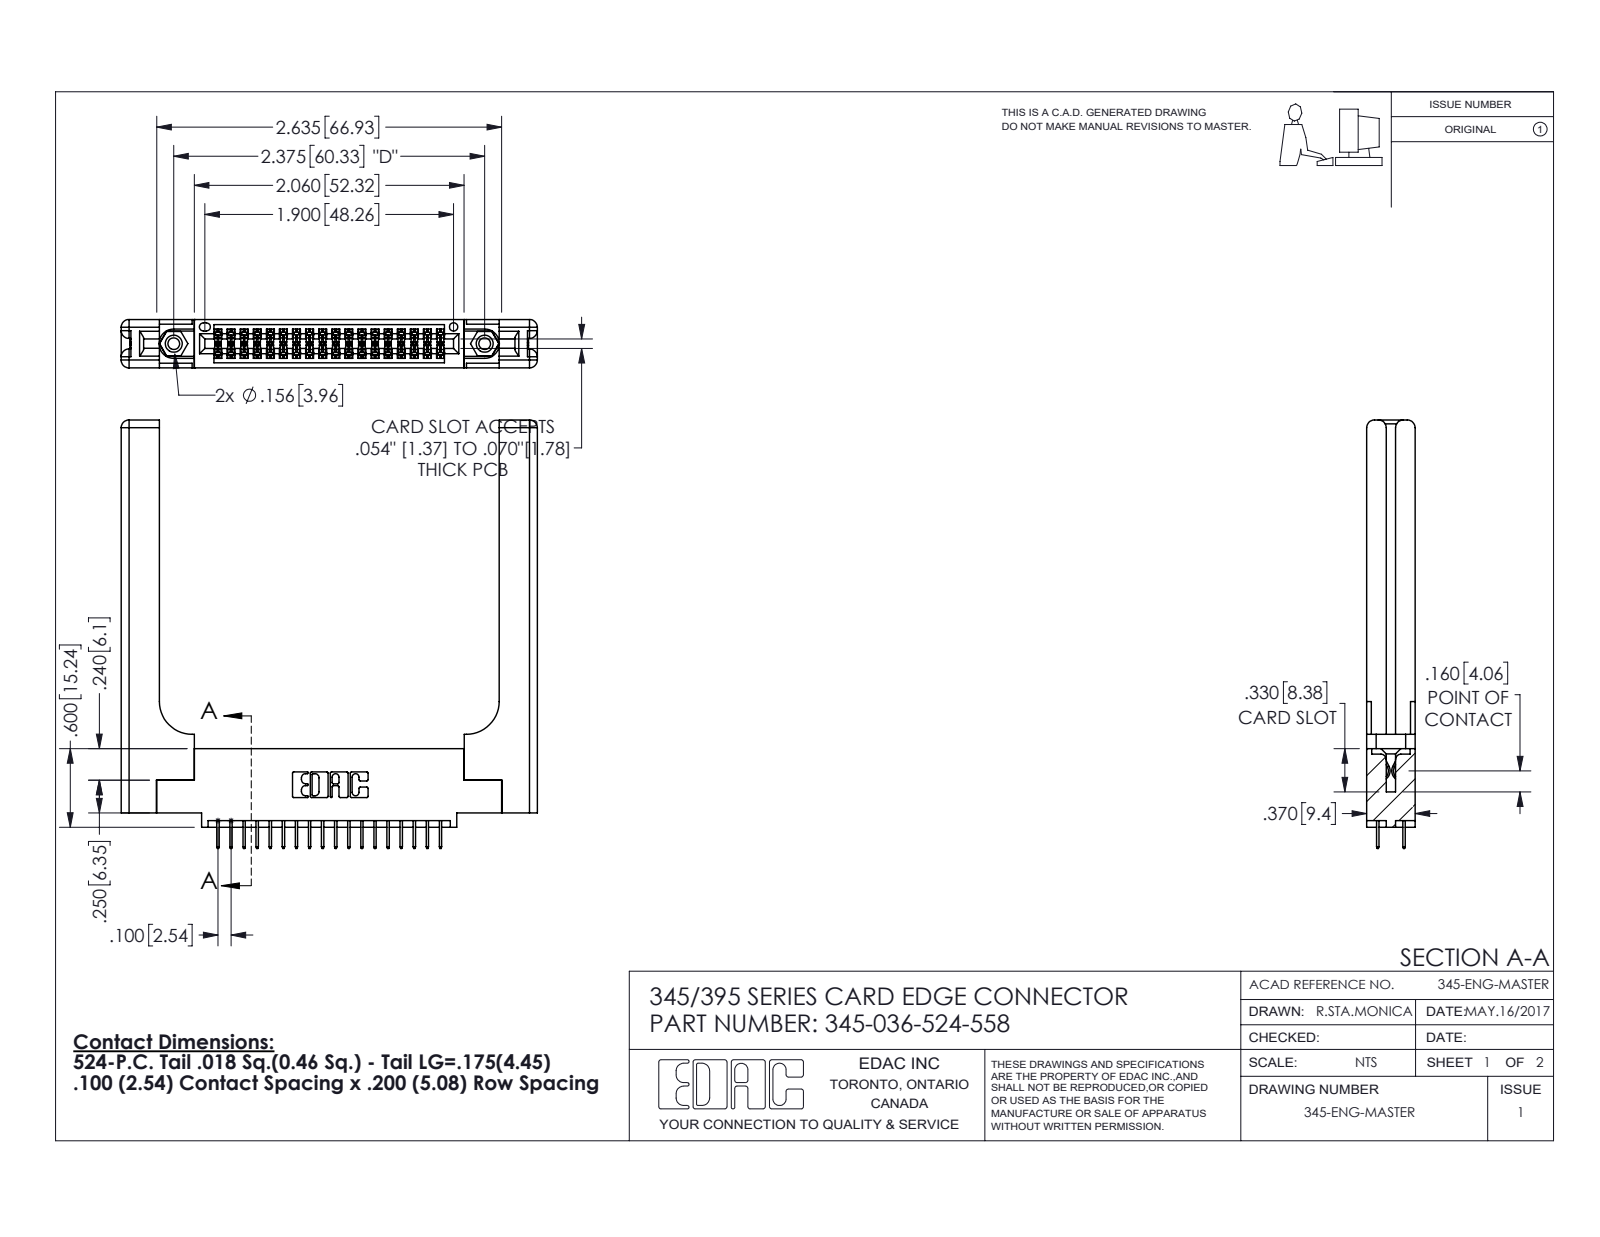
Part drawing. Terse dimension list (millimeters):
name: 345 Part_0.110 Offset - 0.156 Dia-TH; 345-220-058_345-220-058; 345-250-001_345-250-001-102; 345-292-001_345-293-124 (+1 more)
written by: SolidWorks 2016 (CONFIG_CONTROL_DESIGN)
unit: mm
bodies: 41 solids, 2330 faces (1636 planar, 634 cylindrical, 60 other)
size: 83.1 × 80.7 × 9.4
volume: 16 000 mm³; area: 15 620 mm²
holes: 2× ⌀2.3, 2× ⌀3.2, 2× ⌀4, 1× ⌀1.6
bosses: 2× ⌀3.9
rounds: 54× R0.2, 22× R0.3, 16× R1.5, 6× R0.2, 6× R0.8, 3× R0.7, 2× R0.4, 2× R0.5
face distances: 9.4, 1.8, 7.6, 3.8, 3.8, 5.6, 2, 5.1, 2.5, 6.9
hole spacings: 6.9, 54.4, 60.3
